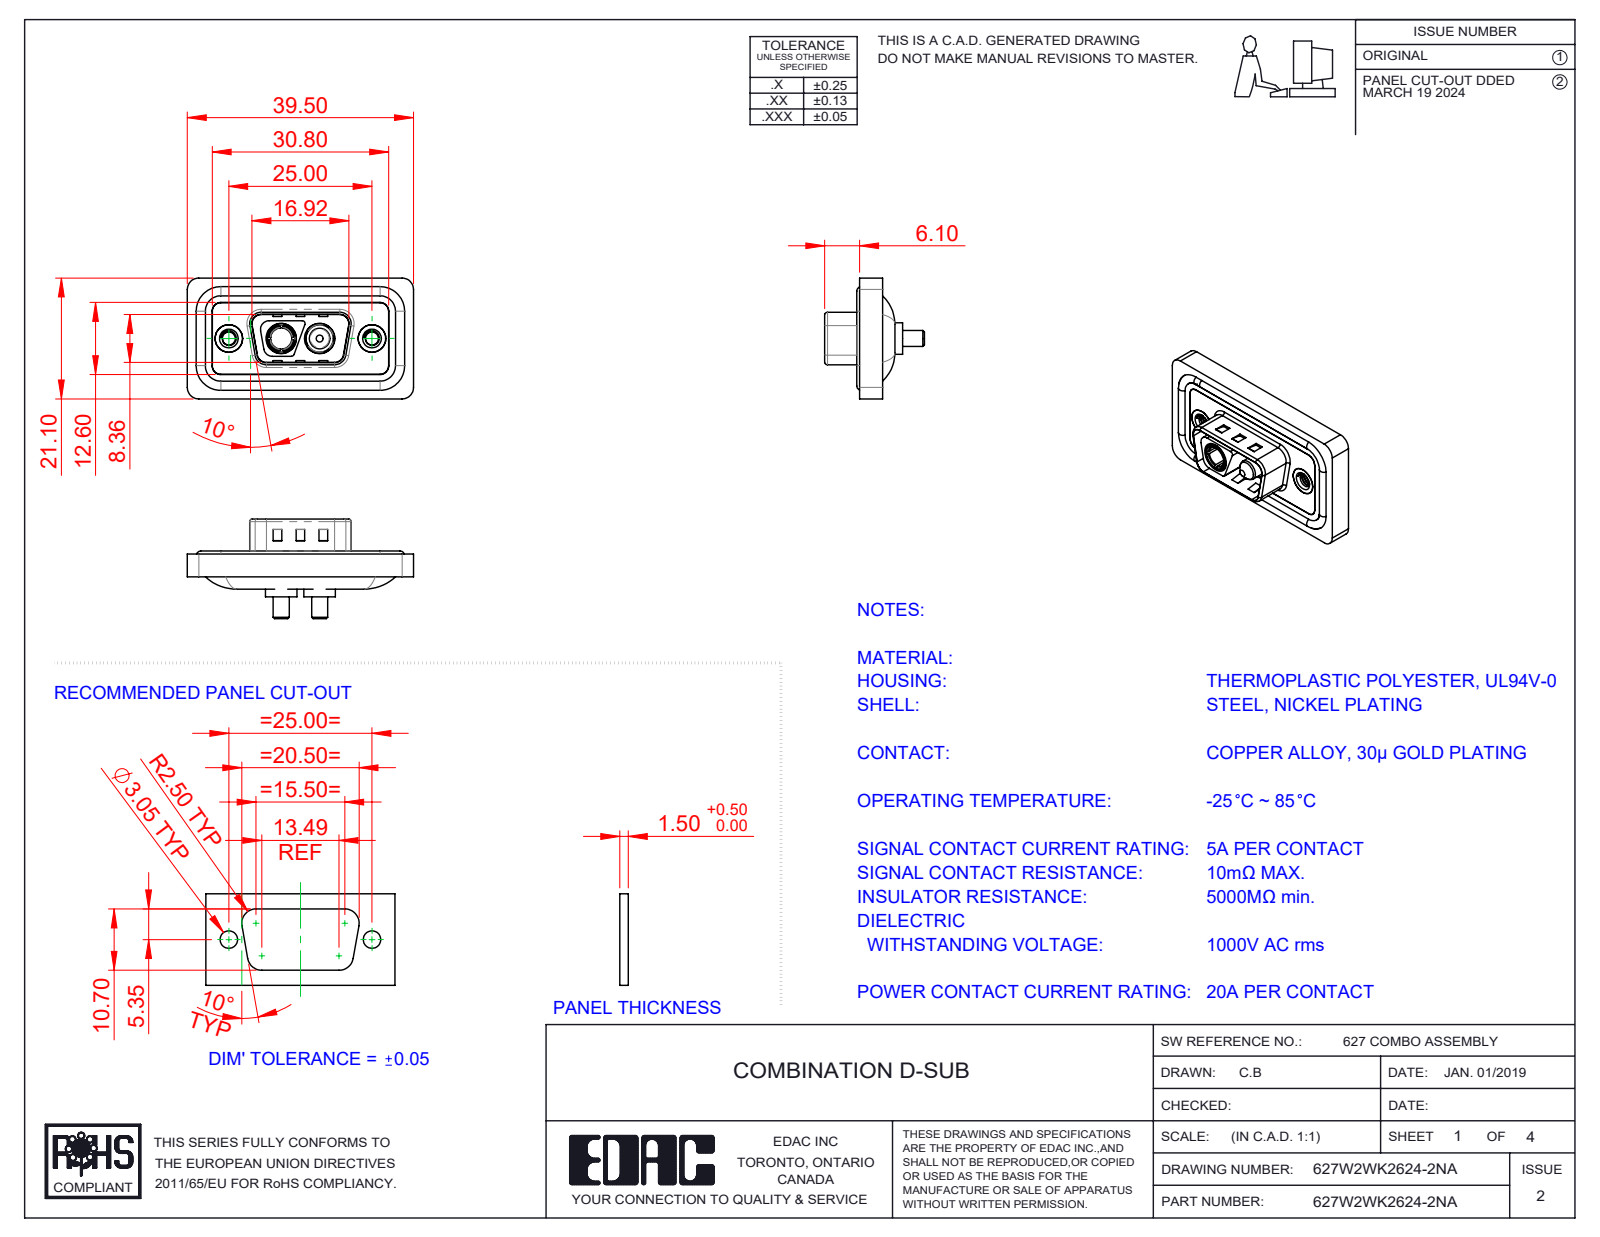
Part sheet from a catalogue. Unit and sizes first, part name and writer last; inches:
Units: inches
Overall size (bounding box): 1.555 × 0.831 × 0.685
Round holes (diameter × count): ⌀0.089 ×2, ⌀0.157 ×2, ⌀0.189 ×2, ⌀0.191 ×2, ⌀0.197 ×2, ⌀0.209 ×2, ⌀0.146 ×1
Round bosses / shafts (diameter × count): ⌀0.063 ×4, ⌀0.217 ×2, ⌀0.205 ×2, ⌀0.193 ×2, ⌀0.187 ×2, ⌀0.148 ×2, ⌀0.11 ×2, ⌀0.195 ×1
Partial cylindrical surfaces — rounded edges, fillets, slot ends (radius × count): R0.059 ×24, R0.079 ×18, R0.02 ×10, R0.063 ×8, R0.01 ×4, R0.024 ×4, R0.026 ×4, R0.035 ×4
Main face-to-face distances: 0.016, 0.043, 0.114, 0.02, 0.122, 0.063, 0.059, 0.157, 0.098, 0.071
Hole centre spacings: 0.36, 0.624, 0.265, 0.984
Volume: 0.278 in³ · Surface area: 11.38 in²
Bodies: 11 solids, 532 faces (189 planar, 229 cylindrical, 114 other)
Part name (STEP PRODUCT): 627Combo Threaded Rivet_A; 627Combo Shell Front_09 Contacts; Power Pin_20A S; 627W2WK2624-2NA (+4 more)
STEP written by: SolidWorks 2023 (CONFIG_CONTROL_DESIGN)
